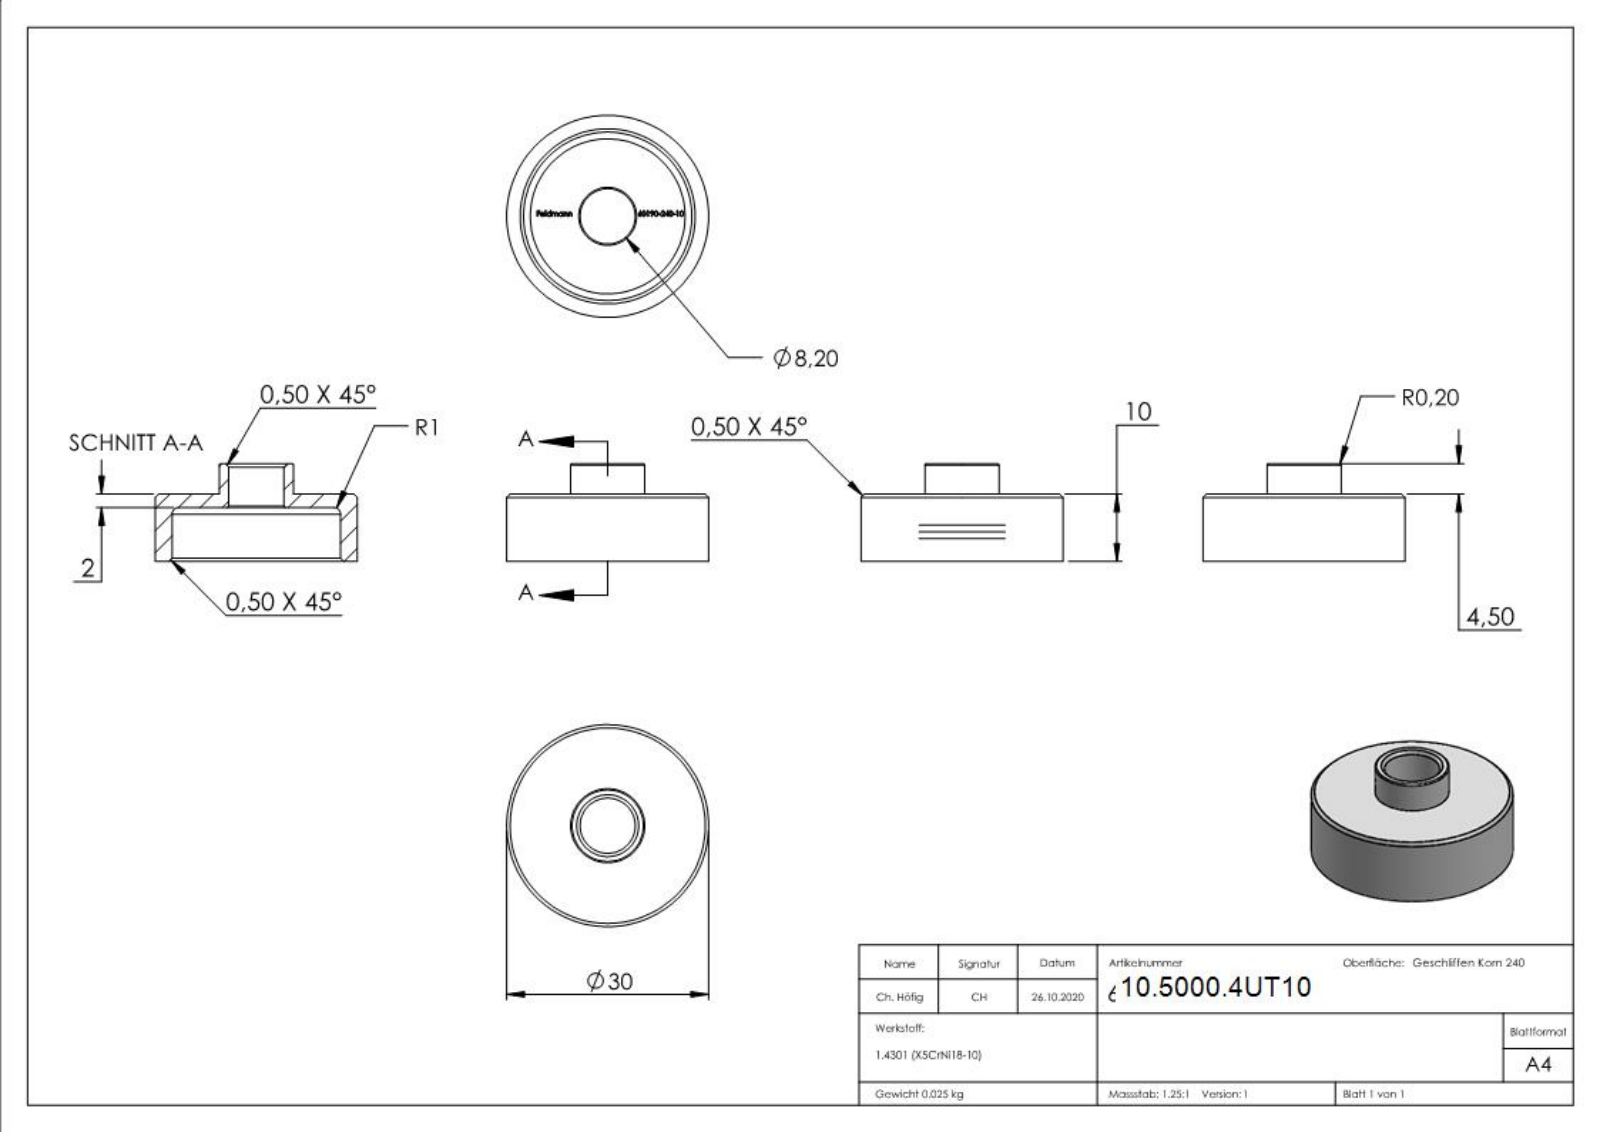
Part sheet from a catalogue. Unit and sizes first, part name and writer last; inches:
Units: inches
Overall size (bounding box): 1.181 × 1.181 × 0.571
Round holes (diameter × count): ⌀0.323 ×1, ⌀0.984 ×1
Round bosses / shafts (diameter × count): ⌀1.181 ×1, ⌀0.433 ×1
Main face-to-face distances: 0.079, 0.315, 0.394, 0.571, 0.256, 0.177, 0.319, 0.075, 0.252, 0.07
Volume: 0.196 in³ · Surface area: 4.822 in²
Bodies: 1 solid, 261 faces (133 planar, 8 cylindrical, 120 other)
Part name (STEP PRODUCT): 60190-240-10
STEP written by: SolidWorks 2018 (CONFIG_CONTROL_DESIGN)
